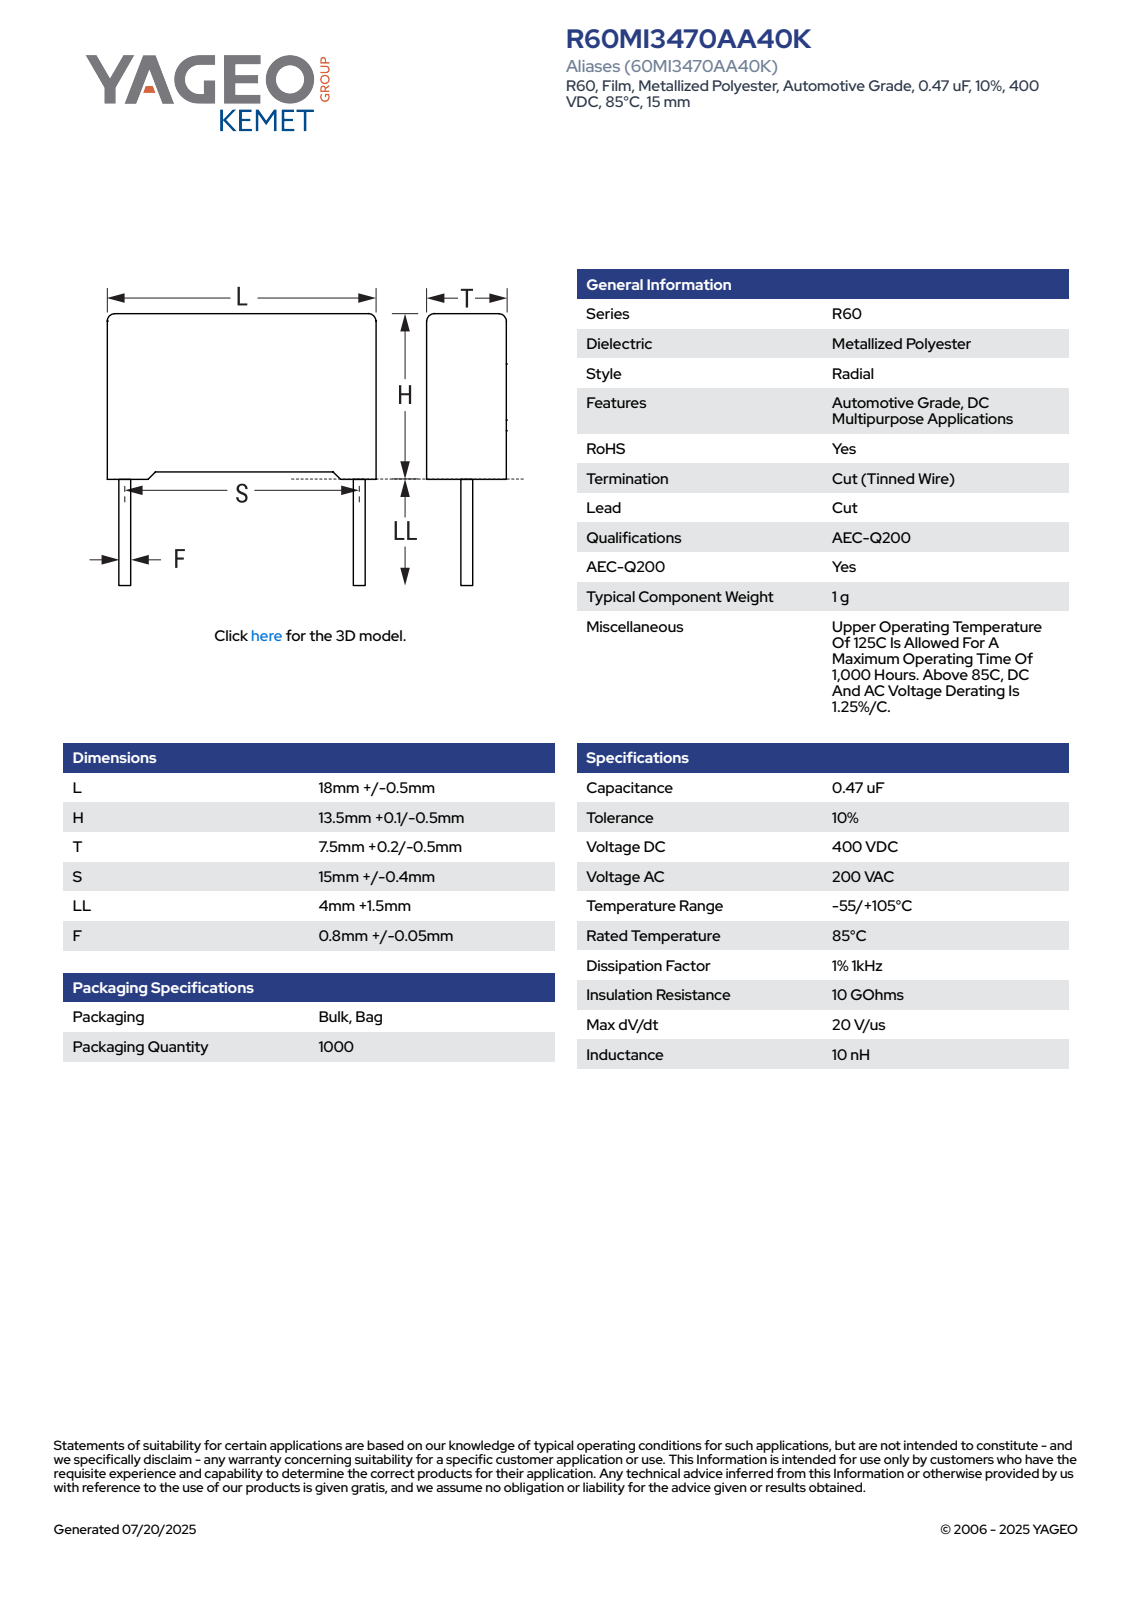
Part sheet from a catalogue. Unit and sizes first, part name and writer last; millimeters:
Units: millimetres
Overall size (bounding box): 19.1 × 18.5 × 7.71
Round bosses / shafts (diameter × count): ⌀0.85 ×2
Partial cylindrical surfaces — rounded edges, fillets, slot ends (radius × count): R0.5 ×4
Main face-to-face distances: 7.7, 12.85, 18.5, 0.62, 0.75, 13.6, 7.08, 0.47, 13.13, 17.88
Volume: 1 851 mm³ · Surface area: 1 060 mm²
Bodies: 4 solids, 85 faces (77 planar, 8 cylindrical, 0 other)
Part name (STEP PRODUCT): CFR_RB2_18X13.5X7.5_L18.5H13.6T7.7S15LL5.5F0.85
STEP written by: SolidWorks 2021 (AUTOMOTIVE_DESIGN)
